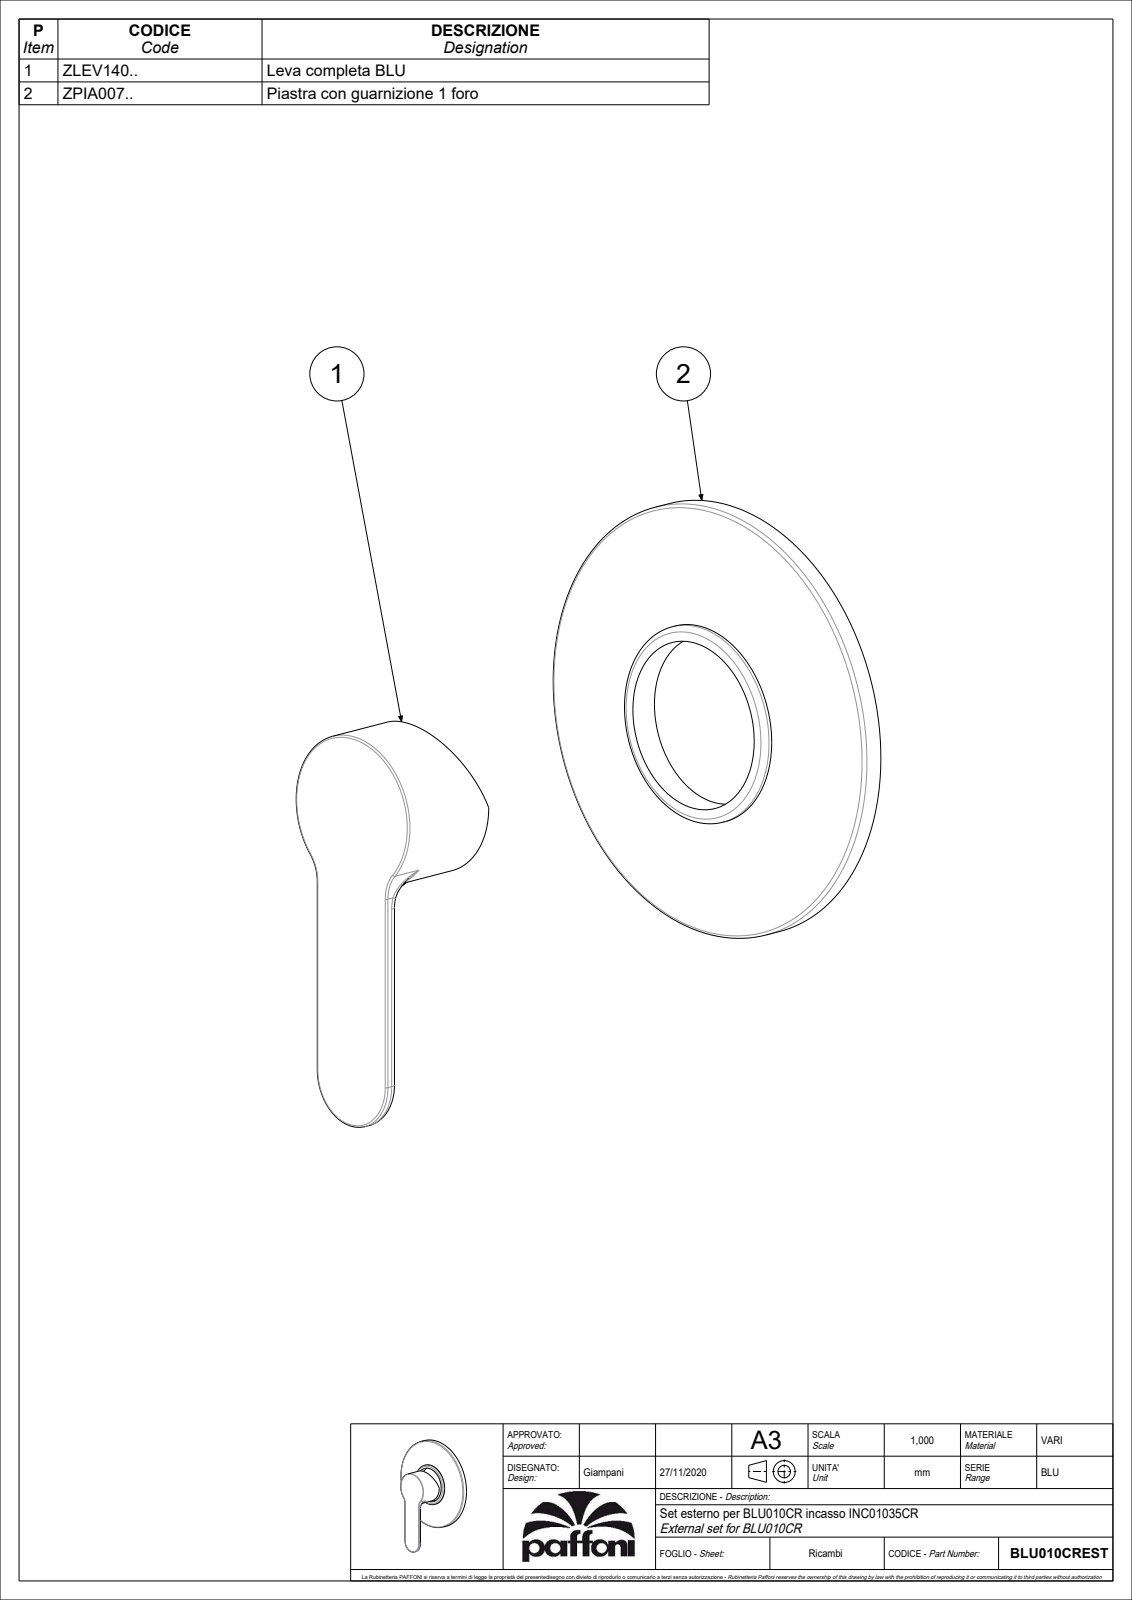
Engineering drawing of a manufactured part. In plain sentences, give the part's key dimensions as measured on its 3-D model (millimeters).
The part is named "BLU010CREST". Its 3-D file was written by "CREO PARAMETRIC BY PTC INC, 2020044 (CONFIG_CONTROL_DESIGN)". It is 2 solids with 169 faces: 54 planar, 66 cylindrical and 49 other. Overall it measures 143 by 116 by 43.5 millimeters. Its volume is 29 511 cubic millimeters and its surface area 39 324 square millimeters. Round holes: 1 of diameter 3, 1 of diameter 3.3, 1 of diameter 4.5, 1 of diameter 45, 1 of diameter 50, 1 of diameter 114. Round bosses or shafts: 1 of diameter 116, 1 of diameter 53, 1 of diameter 42, 1 of diameter 7.6, 1 of diameter 5.5, 1 of diameter 5. Partial cylindrical surfaces (rounded edges, fillets, slot ends): 8 of radius 1.2, 7 of radius 1, 2 of radius 0.5, 2 of radius 1.6, 2 of radius 2.5, 2 of radius 10, 1 of radius 13, 1 of radius 800. The main face-to-face distances are 1, 4, 27.5, 28.5, 11.5, 39, 40, 2.5, 3.5, 8.
